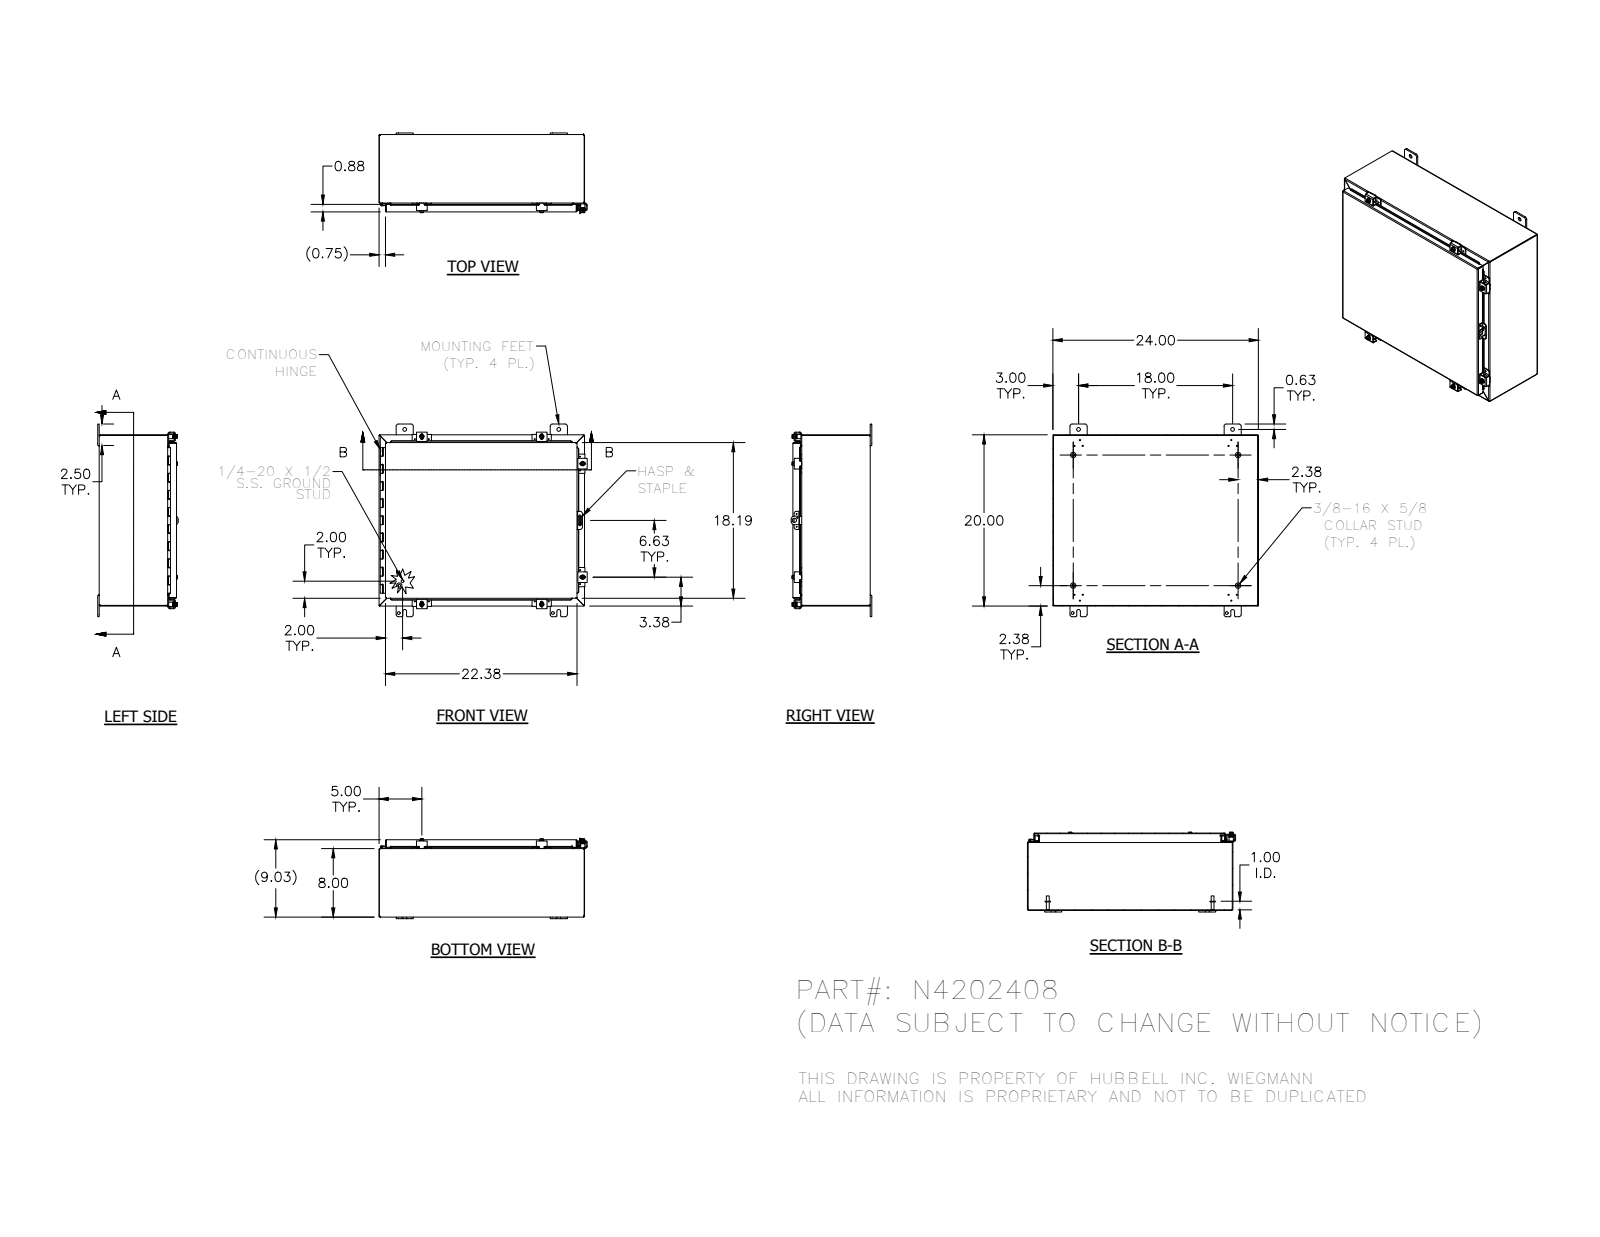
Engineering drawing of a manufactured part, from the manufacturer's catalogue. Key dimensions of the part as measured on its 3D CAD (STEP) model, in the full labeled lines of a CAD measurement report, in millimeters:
Part name (STEP PRODUCT): HFW30825-2_1; 328104L_1; N42024LID_1; 328104T_1 (+8 more)
STEP written by: SolidWorks 2014 (AUTOMOTIVE_DESIGN)
Units: millimetres
Bodies: 47 solids, 2002 faces (767 planar, 894 cylindrical, 341 other)
Overall size (bounding box): 617.5 × 571.5 × 239
Volume: 2 525 000 mm³ · Surface area: 2 588 000 mm²
Round holes (diameter × count): ⌀2.8 ×15, ⌀3 ×12, ⌀5.4 ×6, ⌀7.1 ×6, ⌀7.6 ×6, ⌀8 ×4, ⌀11.1 ×4, ⌀3.2 ×1, ⌀4 ×1, ⌀12.7 ×1
Round bosses / shafts (diameter × count): ⌀6.4 ×8, ⌀13.2 ×6, ⌀12.7 ×6, ⌀8.9 ×6, ⌀15.9 ×4, ⌀8.4 ×4, ⌀2.9 ×2, ⌀8.6 ×1
Partial cylindrical surfaces — rounded edges, fillets, slot ends (radius × count): R0.8 ×71, R1.6 ×43, R3.2 ×35, R6.4 ×31, R0.8 ×23, R2.7 ×23, R3.6 ×12, R1.8 ×8
Main face-to-face distances: 1.9, 227.6, 225.7, 229.4, 506.1, 607.7, 201.3, 26.2, 508, 504.2
Hole centre spacings: 457.2, 22.3, 19.3, 21.3, 23.9, 24.6, 40.5, 50.7
